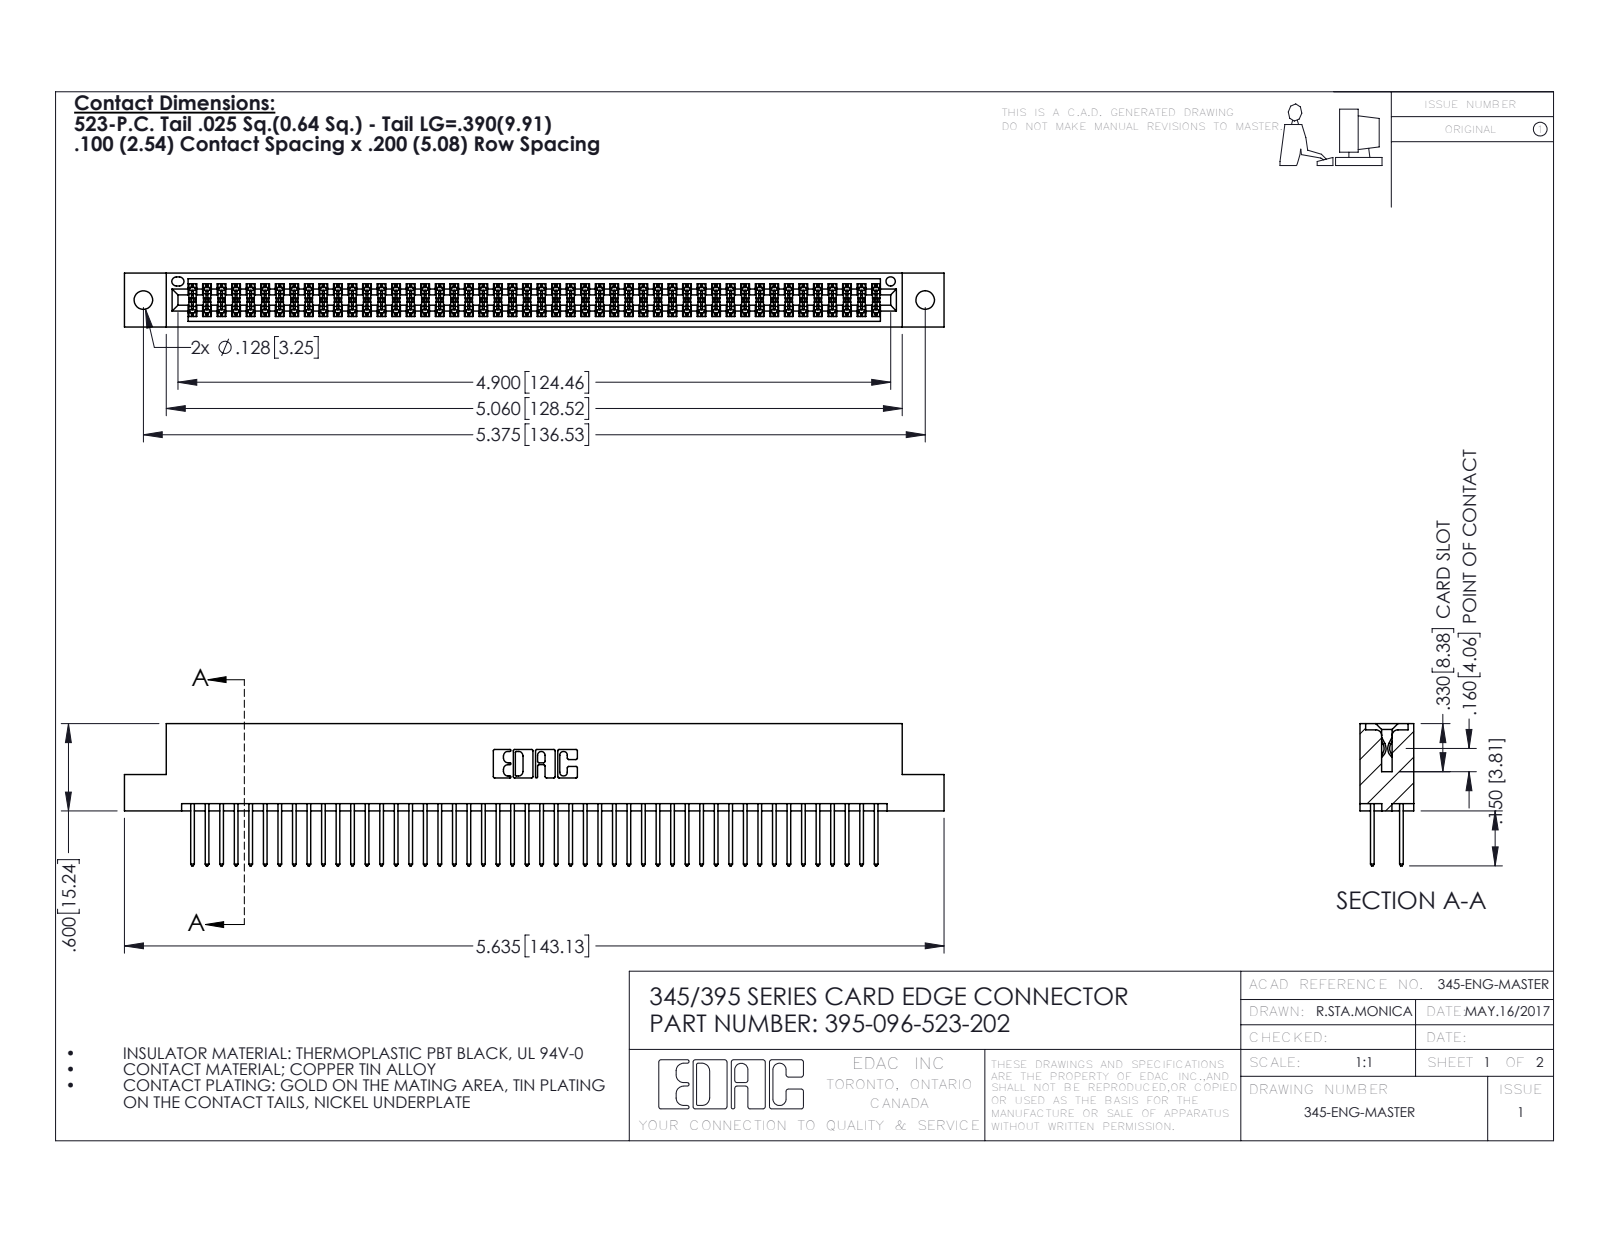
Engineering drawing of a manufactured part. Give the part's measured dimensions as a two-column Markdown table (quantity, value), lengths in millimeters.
| quantity | value |
| --- | --- |
| part name | 395-096-523-202; 345-292-001_345-293-123; 345 Part_Flush Mounting Lugs - 0.128 Dia |
| STEP written by | SolidWorks 2016 (CONFIG_CONTROL_DESIGN) |
| units | millimeters |
| bodies | 97 solids, 4926 faces (3248 planar, 1678 cylindrical, 0 other) |
| overall size | 143.1 × 24.8 × 9.4 |
| volume | 14 100 mm³ |
| surface area | 21 600 mm² |
| round holes (diameter × count) | 3.3 × 2, 1.6 × 1 |
| partial cylindrical surfaces (radius × count) | 0.2 × 144, 0.3 × 96, 0.3 × 22, 0.2 × 6, 0.8 × 6, 0.7 × 3, 0.4 × 2, 0.5 × 2 |
| main face-to-face distances | 7.6, 1.8, 5.1, 2.5, 6.9, 0.6, 9.4, 5.7, 4.4, 3.8 |
| hole center spacings | 6.9, 130.5, 136.5 |
